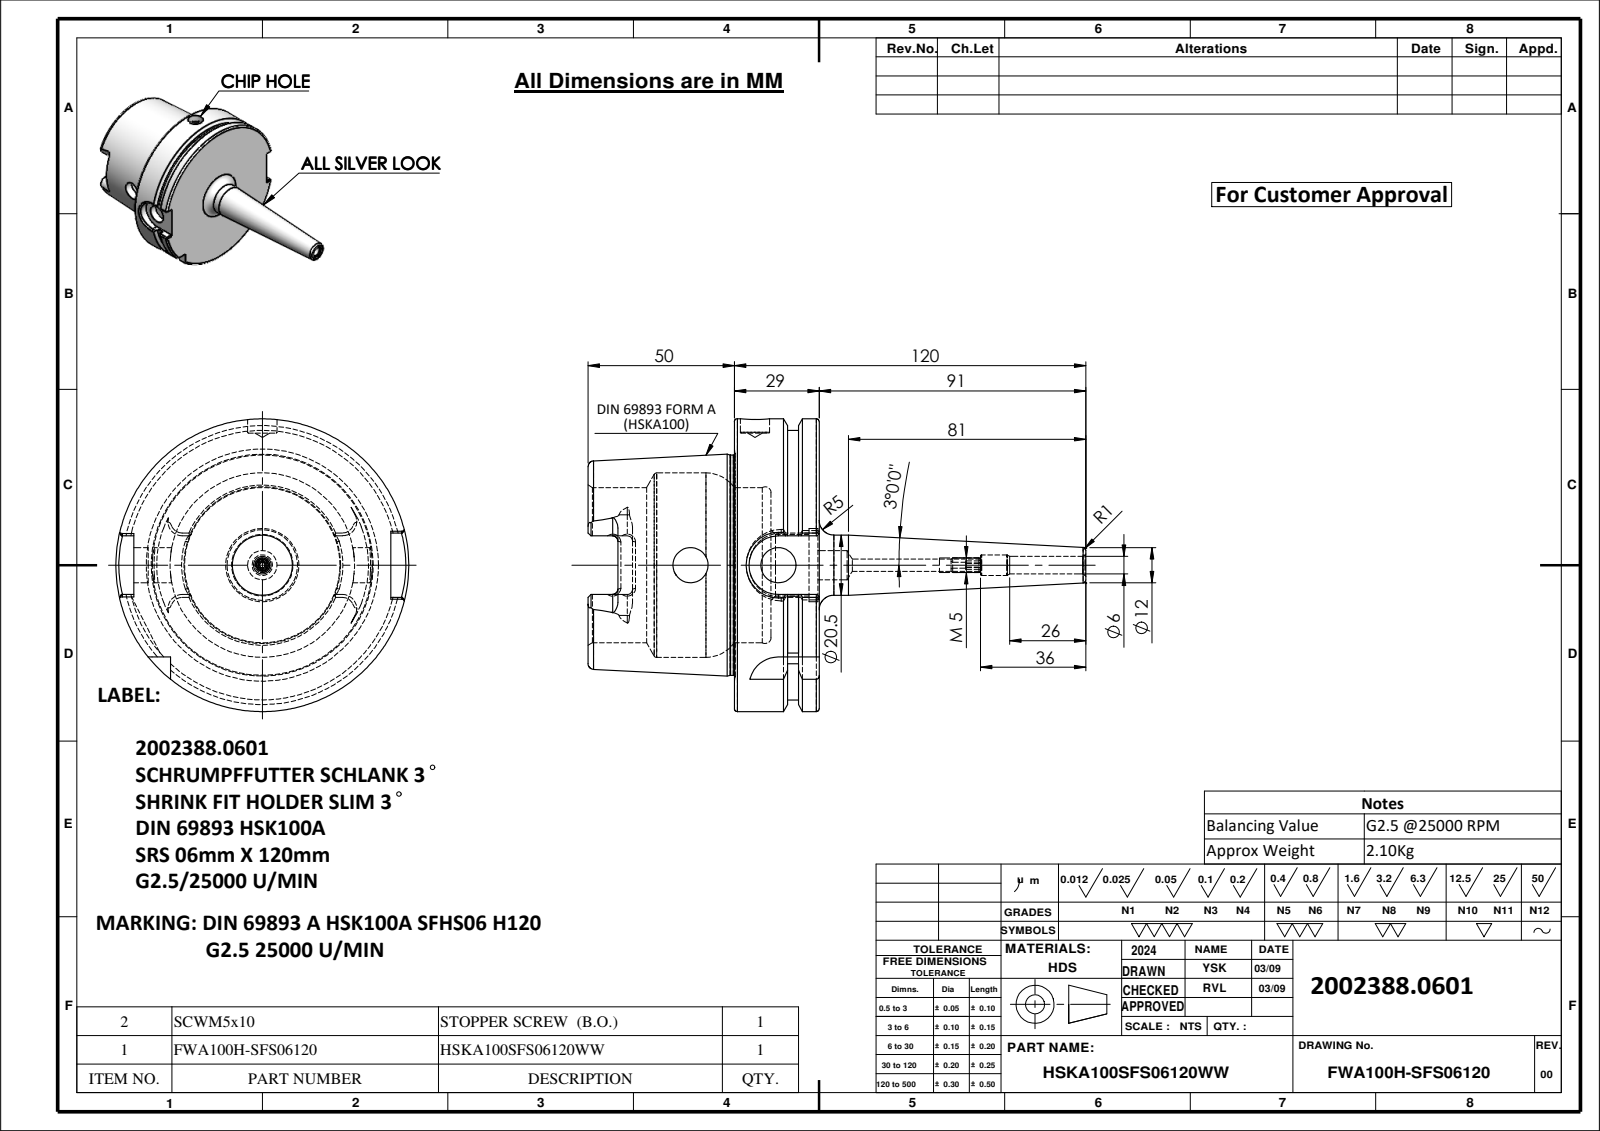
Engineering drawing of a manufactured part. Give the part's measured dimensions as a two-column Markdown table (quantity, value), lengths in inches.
| quantity | value |
| --- | --- |
| part name | SCWM5X10; HSKA100SFS06120WW; FWA100H-SFS06120 |
| STEP written by | SolidWorks 2024 (CONFIG_CONTROL_DESIGN) |
| units | inches |
| bodies | 2 solids, 211 faces (67 planar, 58 cylindrical, 86 other) |
| overall size | 6.693 × 3.937 × 3.937 |
| volume | 16.6 in³ |
| surface area | 87.05 in² |
| round holes (diameter × count) | 0.394 × 2, 0.472 × 2, 0.079 × 1, 0.165 × 1, 0.236 × 1, 0.276 × 1, 0.827 × 1, 0.984 × 1, 2.087 × 1, 2.48 × 1 |
| round bosses / shafts (diameter × count) | 3.937 × 1, 3.622 × 1, 2.959 × 1, 0.807 × 1, 0.197 × 1 |
| partial cylindrical surfaces (radius × count) | 0.071 × 6, 0.192 × 4, 0.394 × 2, 0.433 × 1 |
| main face-to-face distances | 1.14, 0.492, 0.648, 1.969, 2.461, 3.108, 3.091, 1.122, 0.63, 0.018 |
| hole center spacings | 1.181 |
